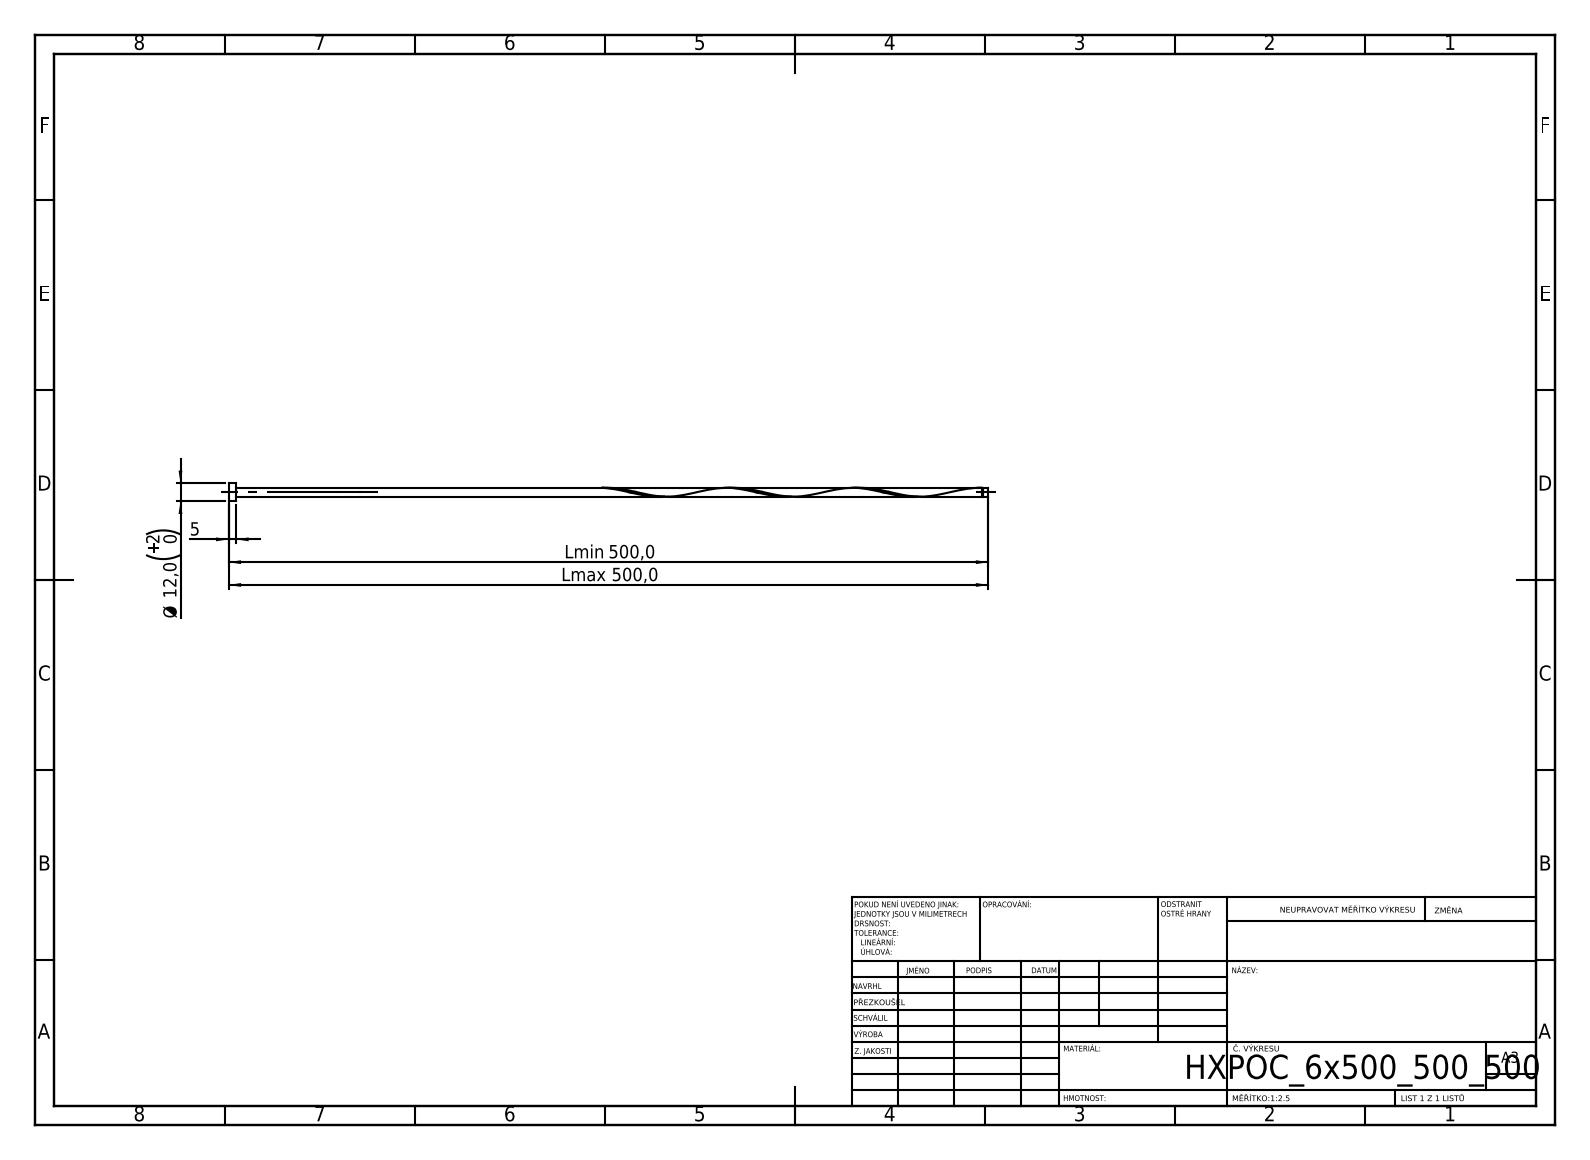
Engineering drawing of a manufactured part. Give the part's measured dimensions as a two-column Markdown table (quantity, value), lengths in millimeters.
| quantity | value |
| --- | --- |
| STEP written by | SolidWorks 2019 (CONFIG_CONTROL_DESIGN) |
| units | millimeters |
| bodies | 1 solid, 16 faces (6 planar, 9 cylindrical, 1 other) |
| overall size | 500 × 12 × 12 |
| volume | 17 555 mm³ |
| surface area | 13 048 mm² |
| round bosses / shafts (diameter × count) | 12 × 1, 6 × 1, 4.8 × 1 |
| main face-to-face distances | 5, 500, 495, 496.71, 491.71, 3.29, 495.51, 490.51, 1.2, 4.49 |
